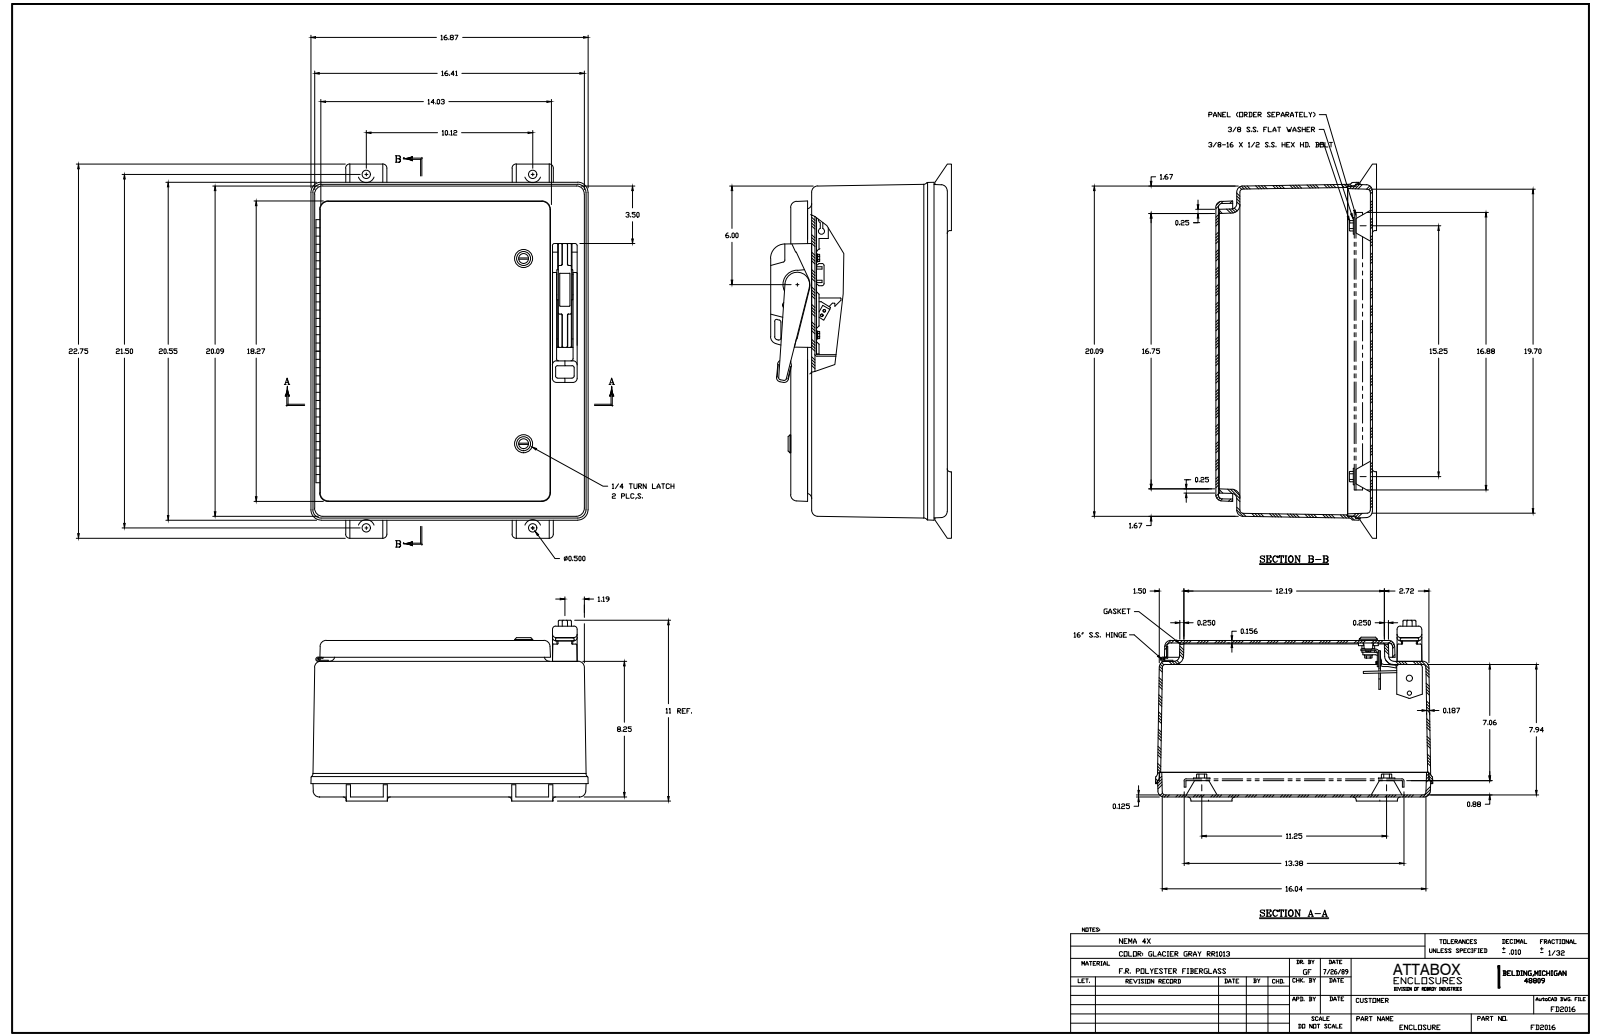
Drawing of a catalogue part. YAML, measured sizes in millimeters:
part_name: "FD2016"
step_written_by: "SolidWorks 2018 (AUTOMOTIVE_DESIGN)"
units: millimeters
bodies: {solids: 86, faces: 2515, planar: 1240, cylindrical: 709, other: 566}
overall_size: [577.9, 428.6, 279.4]
volume: 5123000
surface_area: 2472000
round_holes:
  - {diameter: 3.8, count: 10}
  - {diameter: 4.7, count: 7}
  - {diameter: 6.5, count: 5}
  - {diameter: 4.3, count: 4}
  - {diameter: 5.5, count: 4}
  - {diameter: 7.1, count: 4}
  - {diameter: 7.8, count: 4}
  - {diameter: 7.9, count: 4}
  - {diameter: 7.9, count: 4}
  - {diameter: 11, count: 4}
  - {diameter: 12.7, count: 4}
  - {diameter: 14.3, count: 4}
round_bosses_or_shafts:
  - {diameter: 7.6, count: 6}
  - {diameter: 5.1, count: 6}
  - {diameter: 27.8, count: 4}
  - {diameter: 25.4, count: 4}
  - {diameter: 16, count: 4}
  - {diameter: 9.5, count: 4}
  - {diameter: 9.1, count: 4}
  - {diameter: 7, count: 4}
partial_cylinders:
  - {radius: 6.4, count: 37}
  - {radius: 3.2, count: 20}
  - {radius: 4, count: 17}
  - {radius: 4.8, count: 15}
  - {radius: 8, count: 15}
  - {radius: 12.7, count: 12}
  - {radius: 4.7, count: 10}
  - {radius: 9.5, count: 10}
face_to_face_distances: [4.7, 3.2, 22.2, 212.6, 25.4, 3.3, 242, 238.8, 216.6, 4]
hole_center_spacings: [17.5, 0.4, 7.1, 163.9, 286.5, 19.6, 56.6, 66.1]
